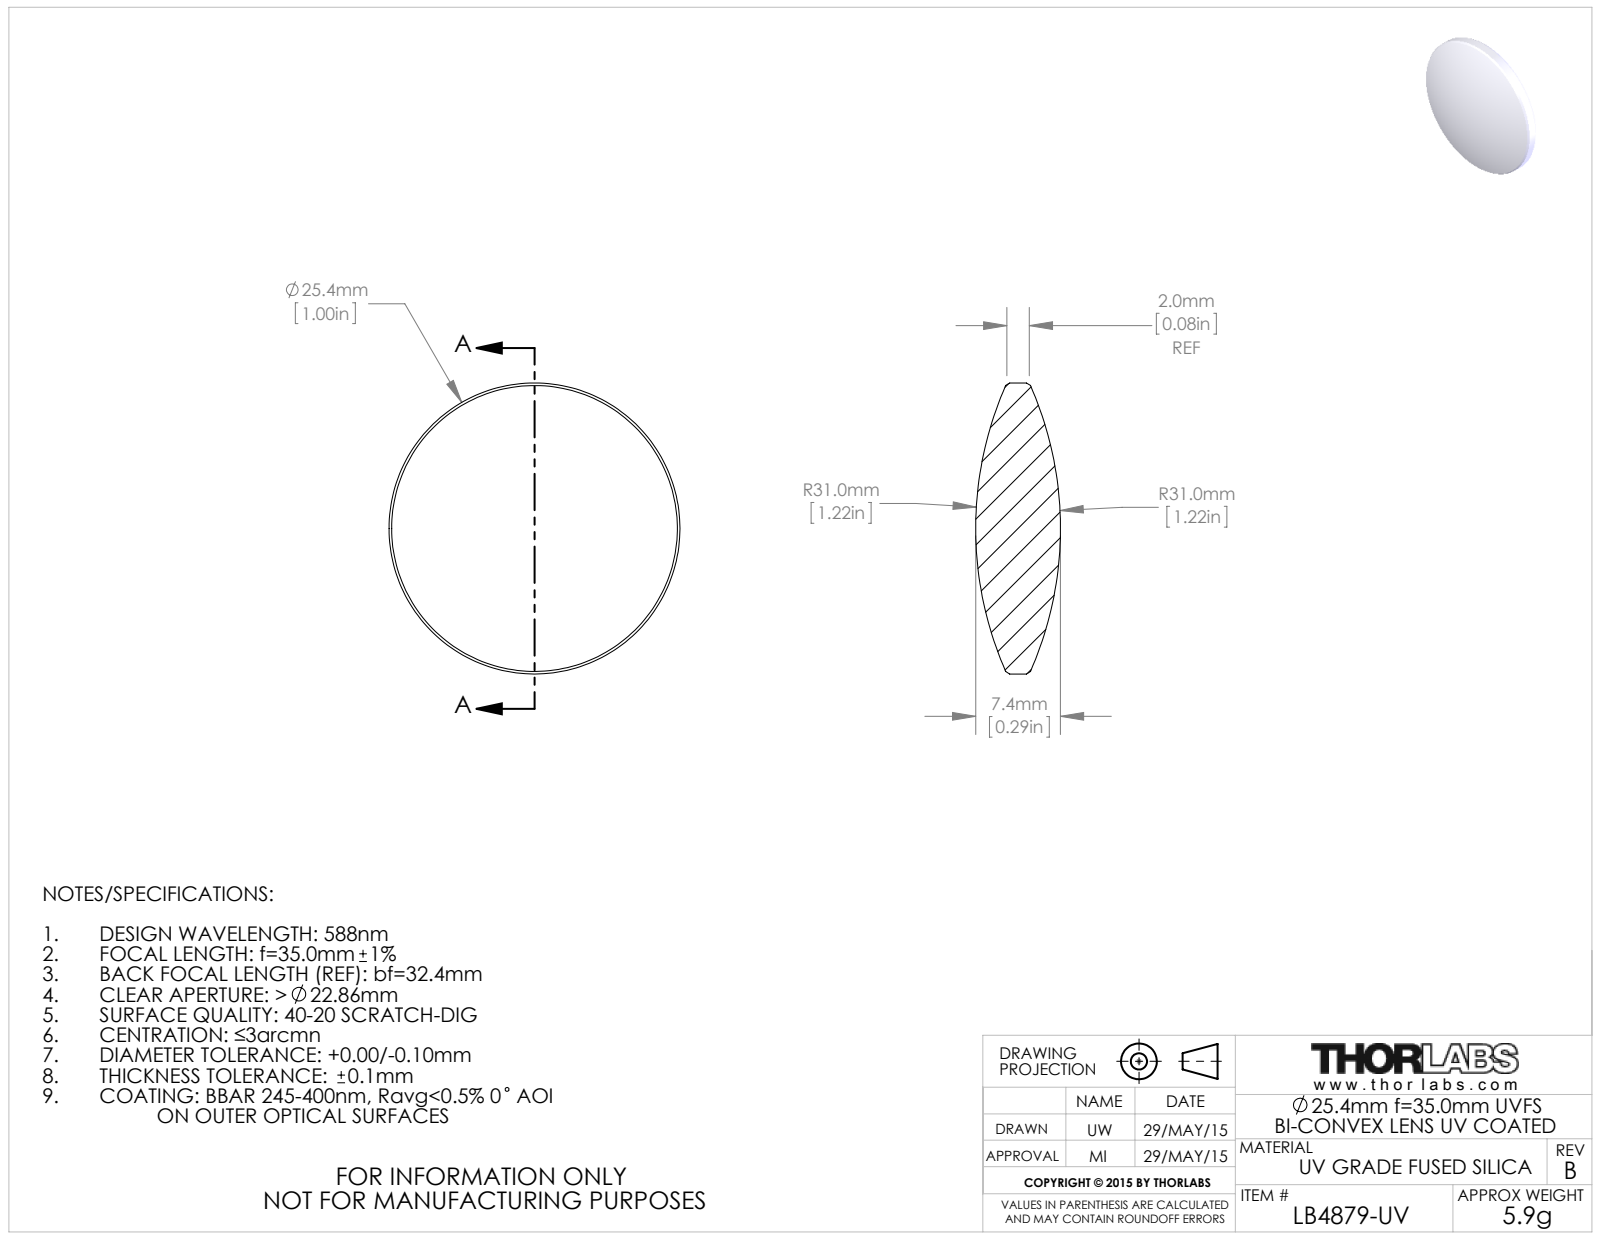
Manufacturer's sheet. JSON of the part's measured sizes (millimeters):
{"part_name": "4317-E0W", "step_written_by": "SolidWorks 2014 (CONFIG_CONTROL_DESIGN)", "units": "millimeters", "bodies": {"solids": 1, "faces": 10, "planar": 0, "cylindrical": 2, "other": 8}, "overall_size": [25.4, 25.4, 7.4], "volume_mm3": 2388, "surface_area_mm2": 1203, "round_bosses_or_shafts": [[25.4, 1]]}
